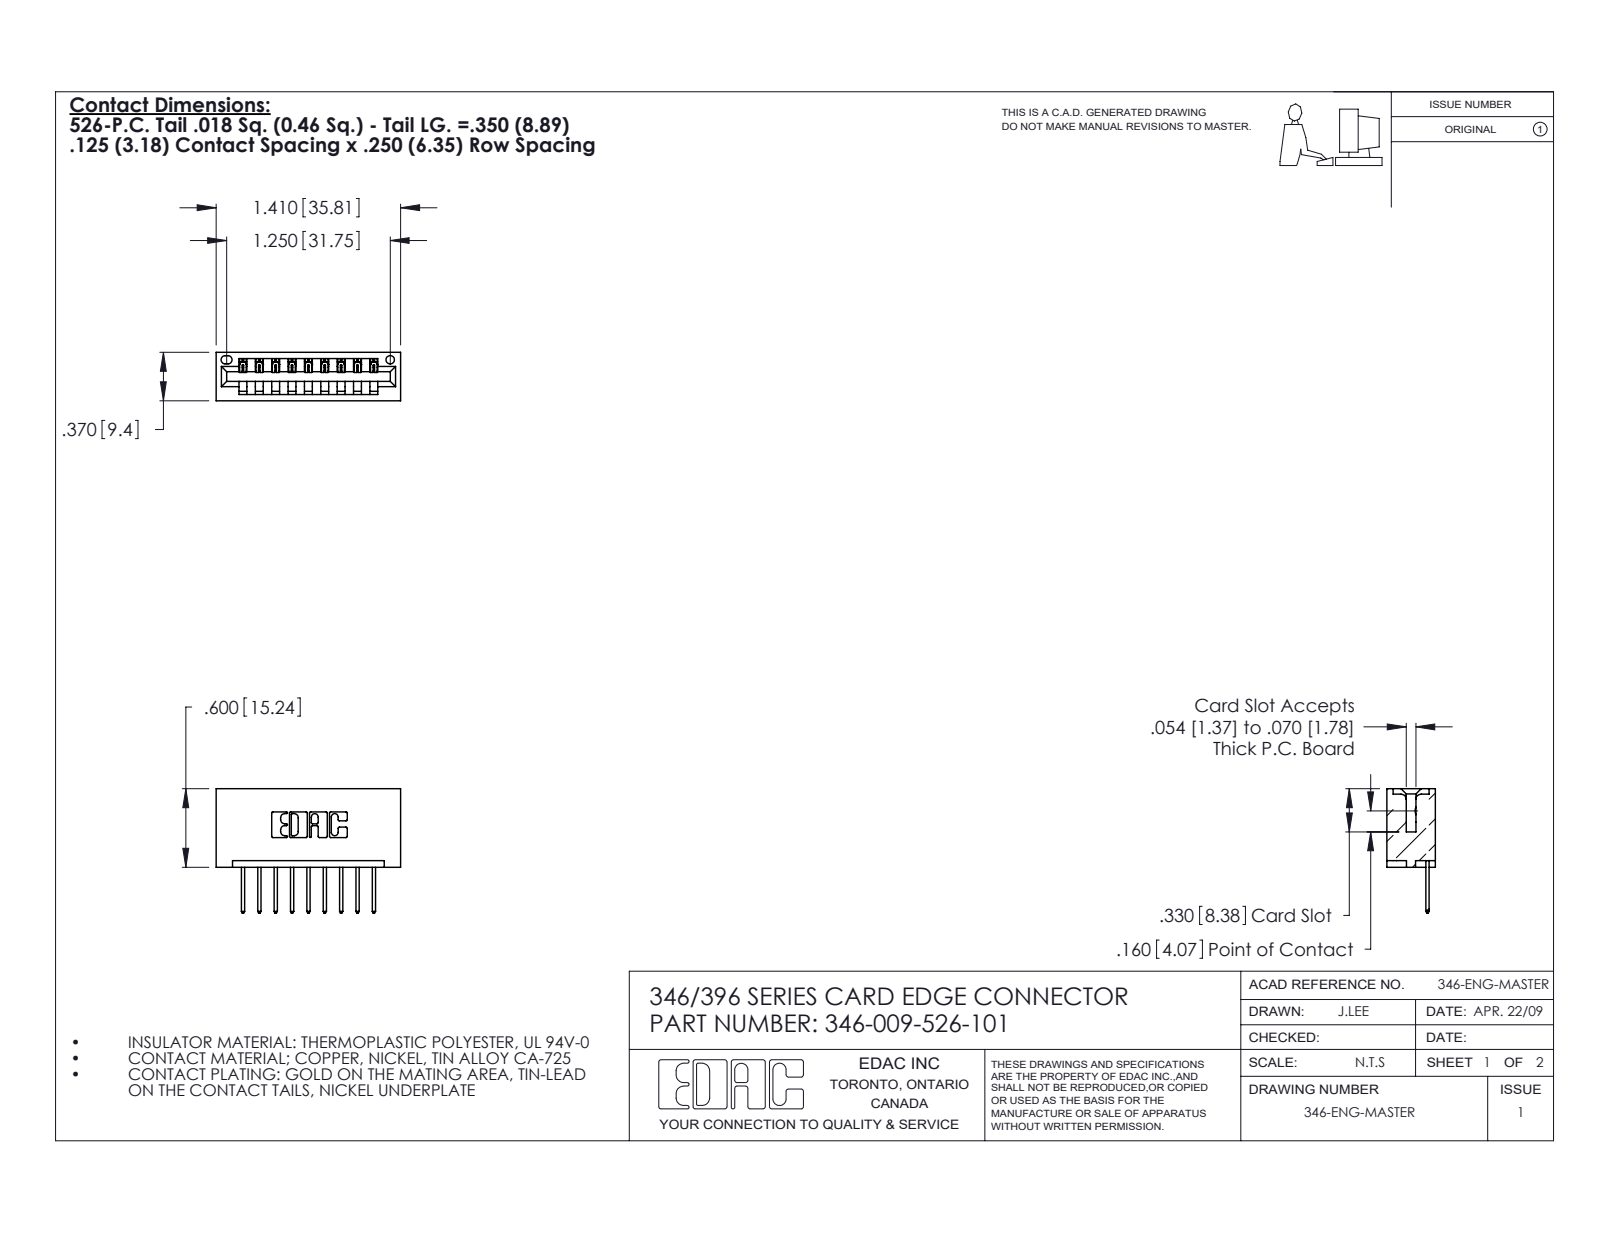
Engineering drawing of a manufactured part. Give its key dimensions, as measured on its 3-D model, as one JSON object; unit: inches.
{"part_name": "346-009-526-101; 345-292-001_345-293-126; 346 Part_No Mounting Lugs", "step_written_by": "SolidWorks 2020 (CONFIG_CONTROL_DESIGN)", "units": "inches", "bodies": {"solids": 10, "faces": 636, "planar": 432, "cylindrical": 204, "other": 0}, "overall_size": [1.41, 0.95, 0.37], "volume_in3": 0.228, "surface_area_in2": 6.802, "round_holes": [[0.064, 1]], "partial_cylinders_radius": [[0.01, 22], [0.006, 18], [0.01, 18], [0.007, 6], [0.031, 6], [0.026, 3], [0.031, 2], [0.04, 2]], "face_to_face_distances": [0.25, 0.048, 0.322, 0.37, 0.5, 0.072, 0.298, 0.025, 0.125, 0.185]}
